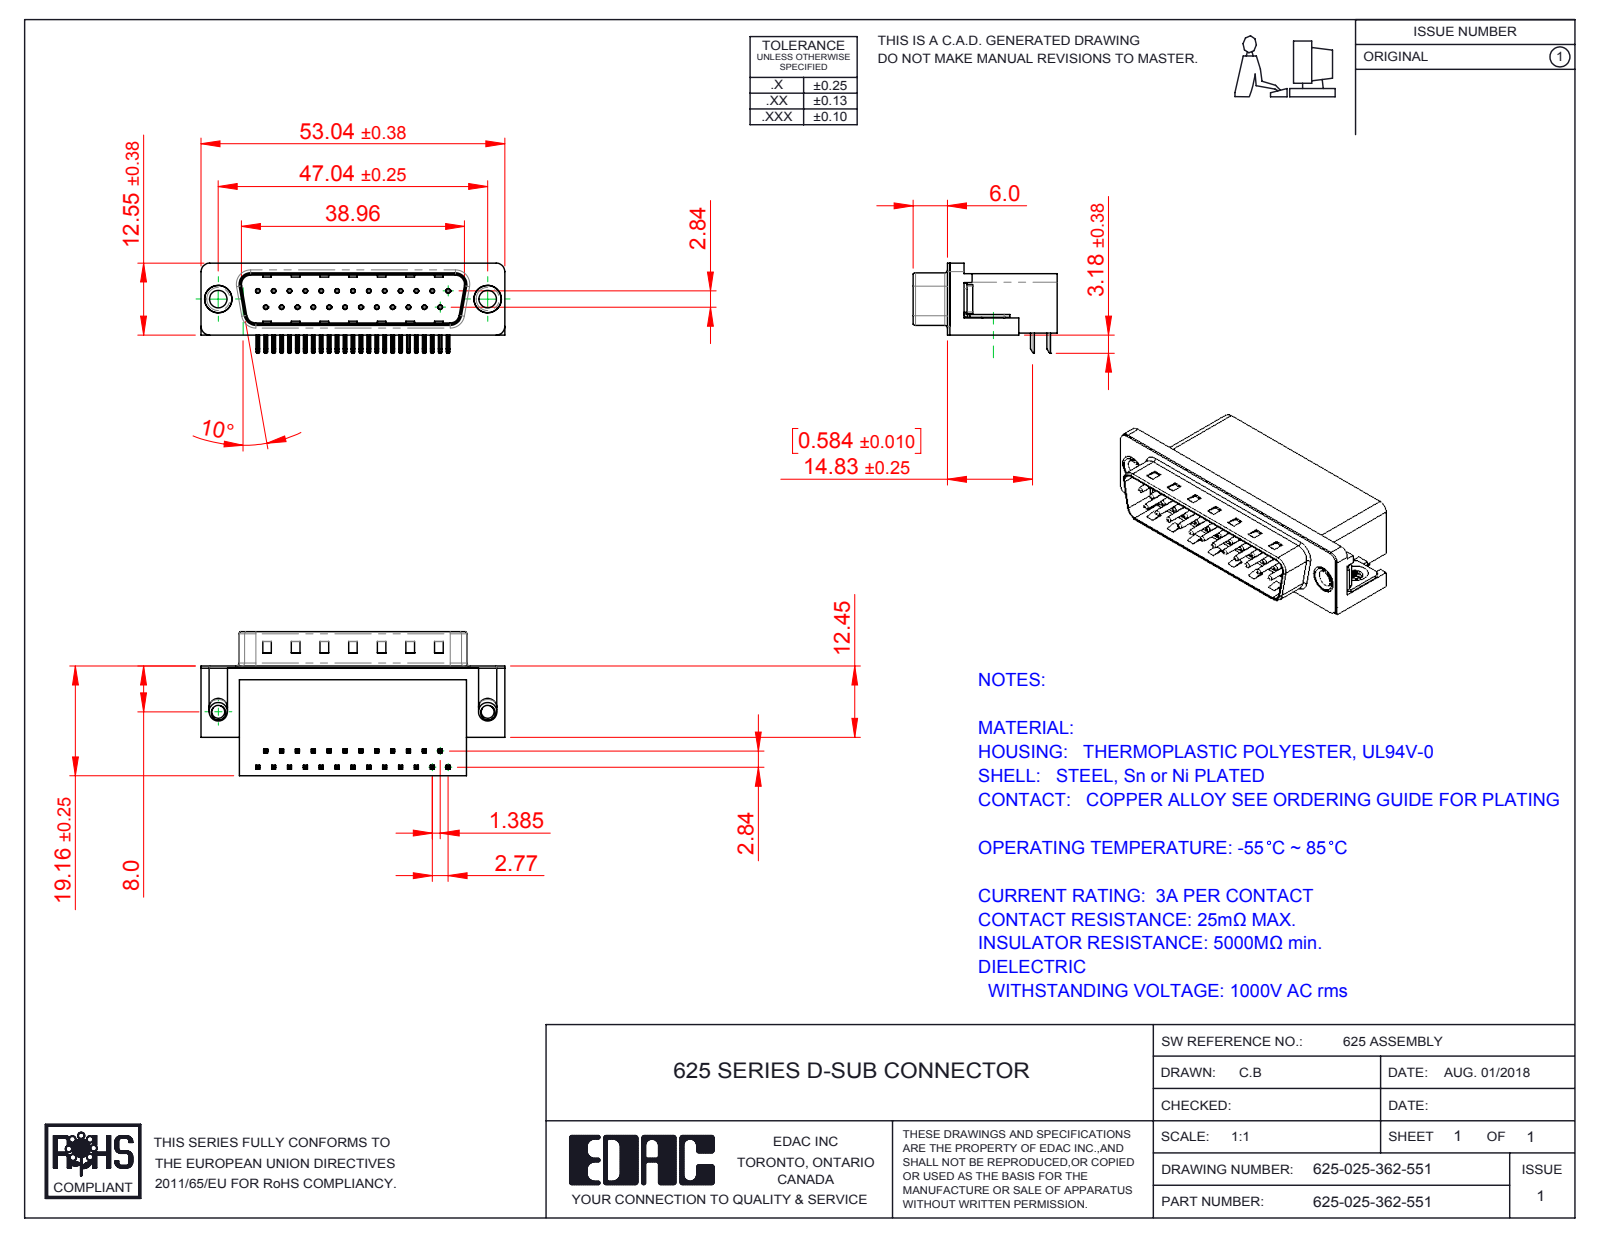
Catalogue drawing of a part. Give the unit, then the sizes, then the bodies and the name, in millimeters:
Units: millimetres
Overall size (bounding box): 53.04 × 25.16 × 15.73
Round holes (diameter × count): ⌀0.35 ×25, ⌀0.8 ×25, ⌀2.26 ×2, ⌀3.05 ×2, ⌀4 ×2, ⌀4.8 ×2, ⌀5 ×2
Round bosses / shafts (diameter × count): ⌀0.75 ×25, ⌀4.9 ×2, ⌀4.75 ×2, ⌀3.85 ×2, ⌀3.26 ×2
Partial cylindrical surfaces — rounded edges, fillets, slot ends (radius × count): R0.25 ×108, R0.12 ×50, R1 ×16, R0.5 ×9, R1.6 ×8, R1.5 ×7, R0.9 ×4, R2 ×4
Main face-to-face distances: 0.4, 10.35, 18.76, 2.1, 8.76, 10.46, 10.86, 1.7, 19.16, 10.11
Hole centre spacings: 3.16, 2.77, 11.08, 5.54, 8.31, 5.03, 13.85, 7.48
Volume: 9 163 mm³ · Surface area: 8 918 mm²
Bodies: 31 solids, 2257 faces (1407 planar, 655 cylindrical, 195 other)
Part name (STEP PRODUCT): 625 Contact Top; 625 Thru Hole Rivet; 625-025-362-551; 625 Shell_25 Socket (+3 more)
STEP written by: SolidWorks 2016 (CONFIG_CONTROL_DESIGN)
